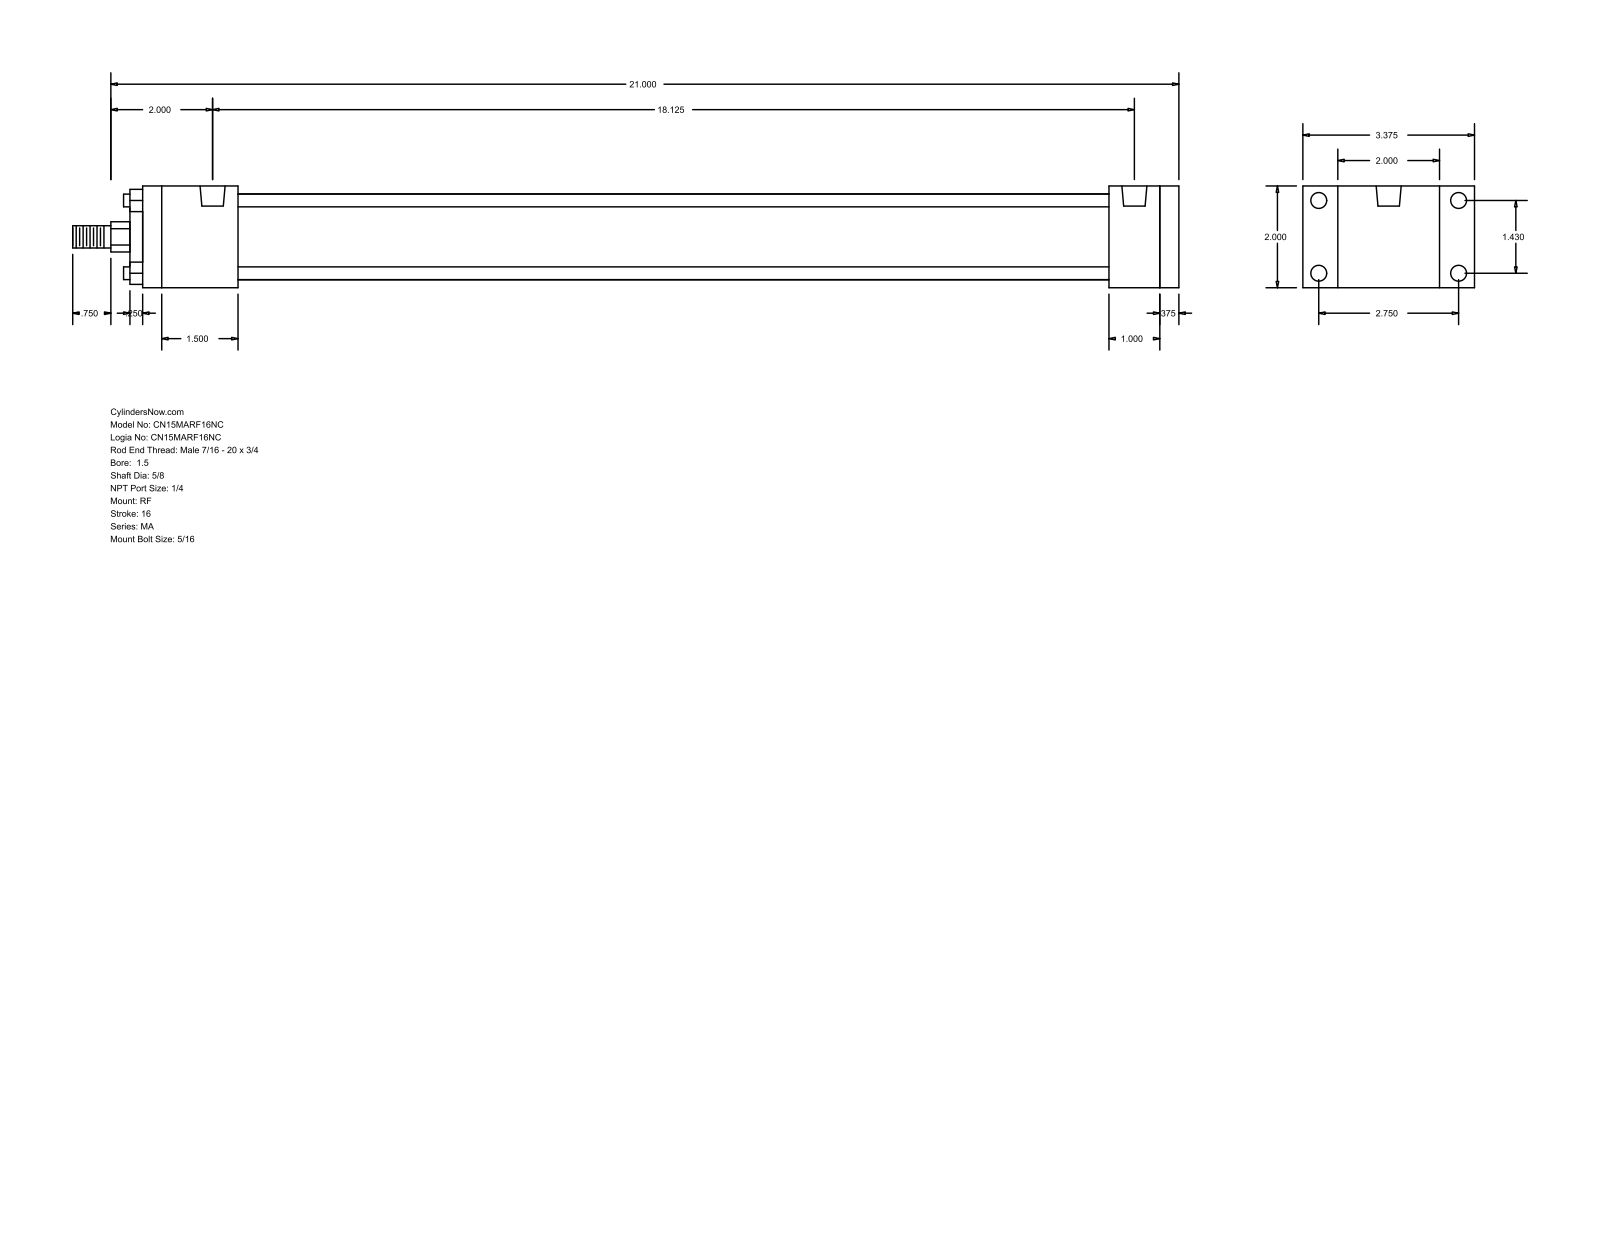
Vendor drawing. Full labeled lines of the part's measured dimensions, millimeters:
Part name (STEP PRODUCT): MA_RF__0150_0.625
STEP written by: GSSL Pune (CONFIG_CONTROL_DESIGN)
Units: millimetres
Bodies: 0 solids, 92 faces (64 planar, 28 cylindrical, 0 other)
Overall size (bounding box): 552.45 × 85.72 × 50.8
Round holes (diameter × count): ⌀7.94 ×8, ⌀12.49 ×2
Round bosses / shafts (diameter × count): ⌀6.35 ×4, ⌀42.93 ×1, ⌀28.57 ×1, ⌀15.88 ×1, ⌀11.11 ×1
Partial cylindrical surfaces — rounded edges, fillets, slot ends (radius × count): R7.54 ×1
Main face-to-face distances: 50.8, 9.52, 508, 517.52, 25.4, 482.6, 34.92, 47.62, 434.98, 460.38
Hole centre spacings: 36.32, 69.84, 78.72, 460.38
